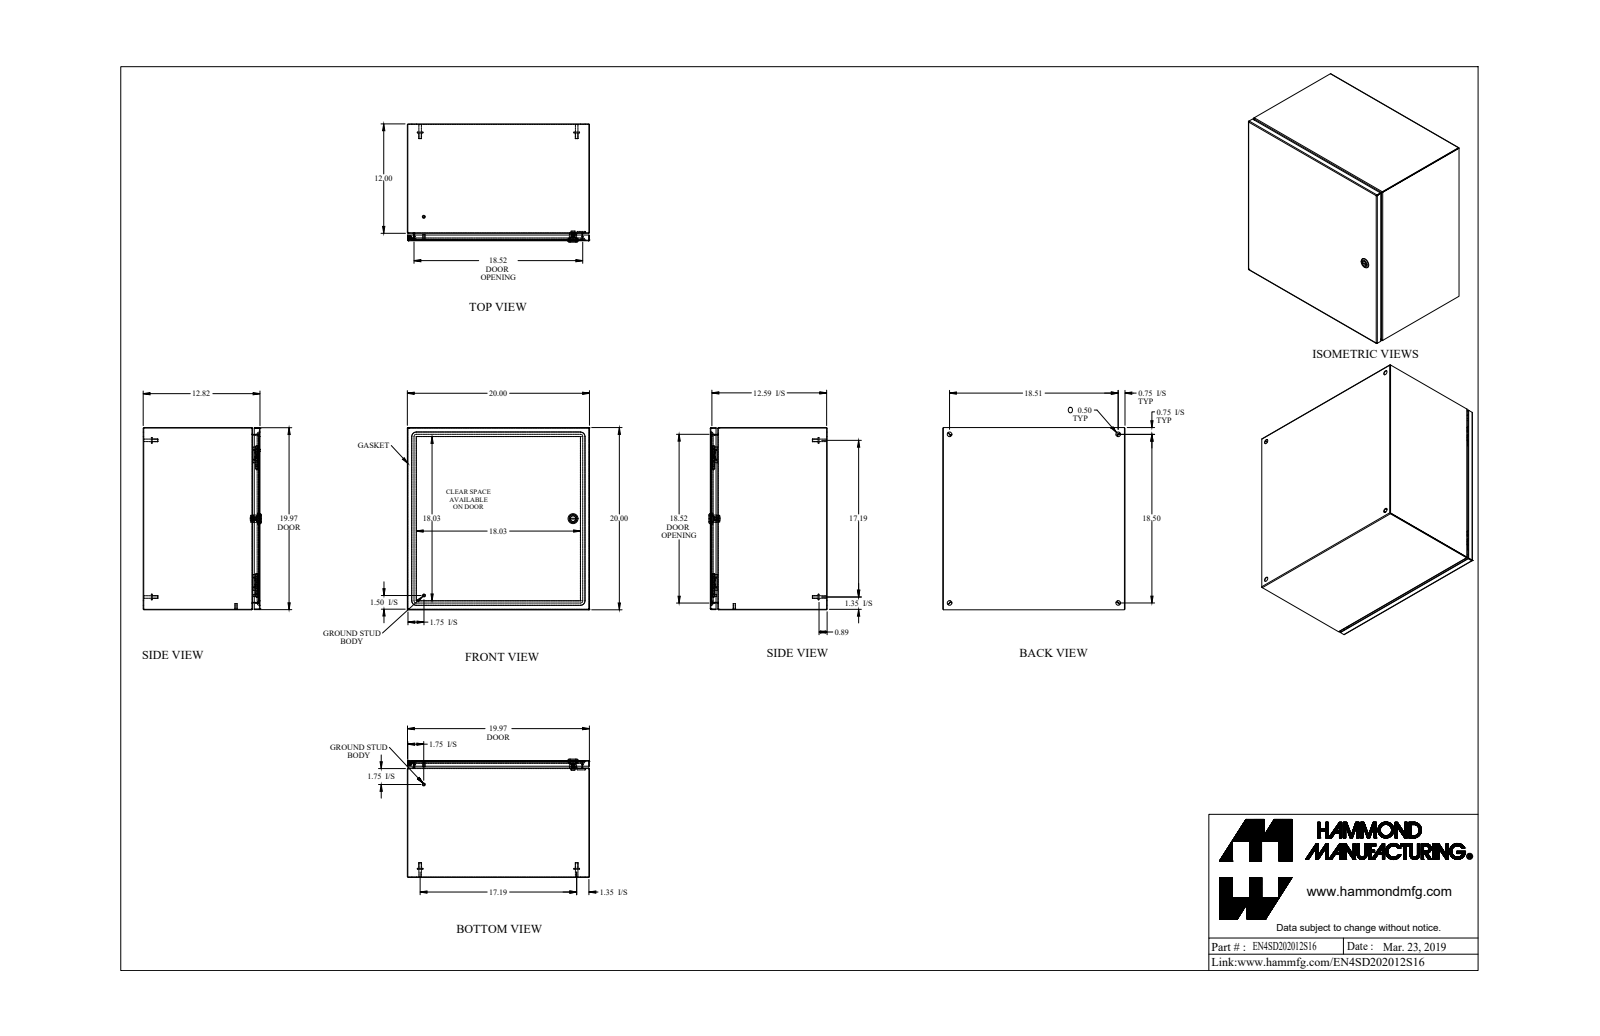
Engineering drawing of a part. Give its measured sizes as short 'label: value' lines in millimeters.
name: EN4SD202012S16_Default
written by: SolidWorks 2019 (CONFIG_CONTROL_DESIGN)
unit: mm
bodies: 24 solids, 644 faces (303 planar, 207 cylindrical, 134 other)
size: 508 × 508 × 329.7
volume: 1 916 000 mm³; area: 2 588 000 mm²
holes: 5× ⌀12.7, 1× ⌀4.4, 1× ⌀5, 1× ⌀6.1, 1× ⌀6.1, 1× ⌀9.8, 1× ⌀16, 1× ⌀19.5
bosses: 6× ⌀8, 5× ⌀15.9, 4× ⌀7, 2× ⌀6.4, 1× ⌀27.9, 1× ⌀19.9, 1× ⌀13.3, 1× ⌀12.1
rounds: 19× R0.7, 19× R2.2, 12× R4.8, 4× R0.2, 4× R1.6, 4× R6.4, 4× R12.7, 2× R3.2
face distances: 1.4, 506.6, 505.1, 508, 1.4, 322.8, 324.2, 324.2, 325.7, 303.4
hole spacings: 236.5, 469.9, 470.3, 501.4, 664.8
